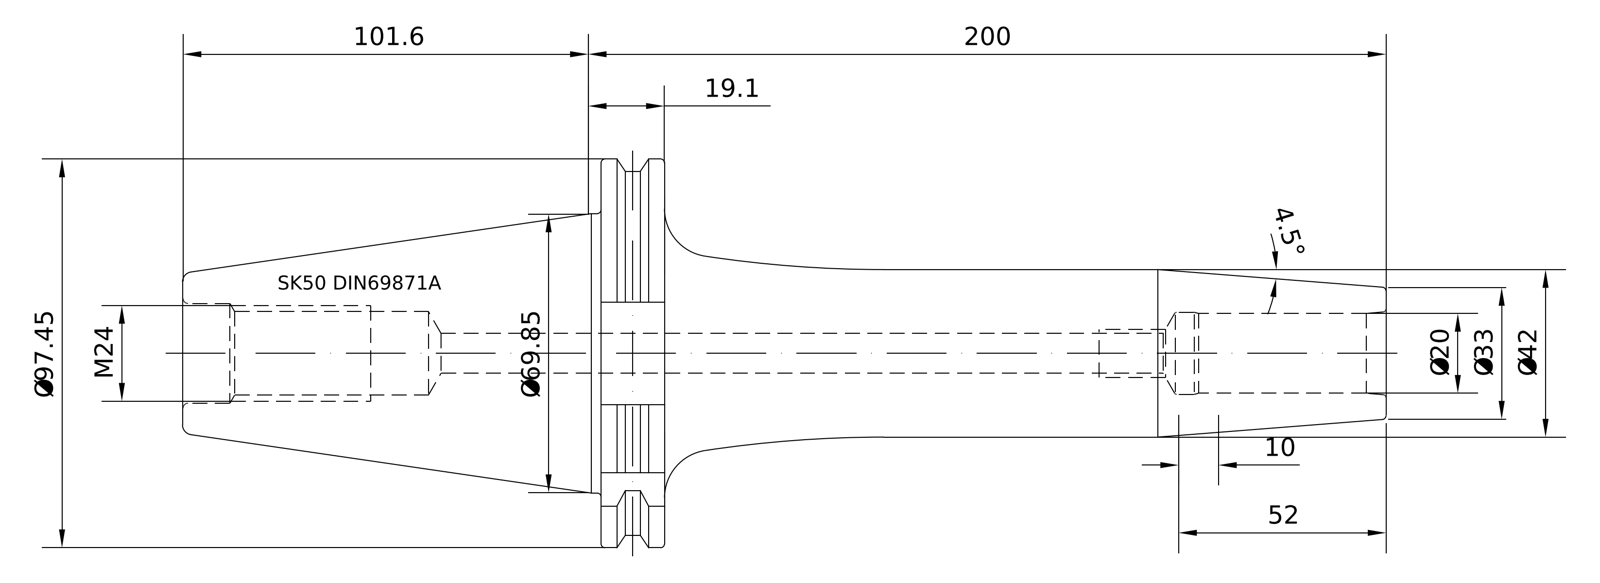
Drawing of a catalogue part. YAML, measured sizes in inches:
part_name: "50-446-20"
step_written_by: "PRO/ENGINEER BY PARAMETRIC TECHNOLOGY CORPORATION, 2010430 (CONFIG_CONTROL_DESIGN)"
units: inches
bodies: {solids: 1, faces: 95, planar: 21, cylindrical: 24, other: 50}
overall_size: [11.874, 3.837, 3.701]
volume: 35.07
surface_area: 105.1
round_holes:
  - {diameter: 0.787, count: 1}
  - {diameter: 0.817, count: 1}
  - {diameter: 0.985, count: 1}
  - {diameter: 1.012, count: 1}
round_bosses_or_shafts:
  - {diameter: 3.583, count: 1}
  - {diameter: 2.722, count: 1}
  - {diameter: 1.654, count: 1}
  - {diameter: 0.945, count: 1}
partial_cylinders:
  - {radius: 0.069, count: 1}
  - {radius: 1.919, count: 1}
face_to_face_distances: [0.624, 7.748, 7.124, 2.866, 4.126, 4.75, 11.874, 9.827, 5.701, 5.077]
